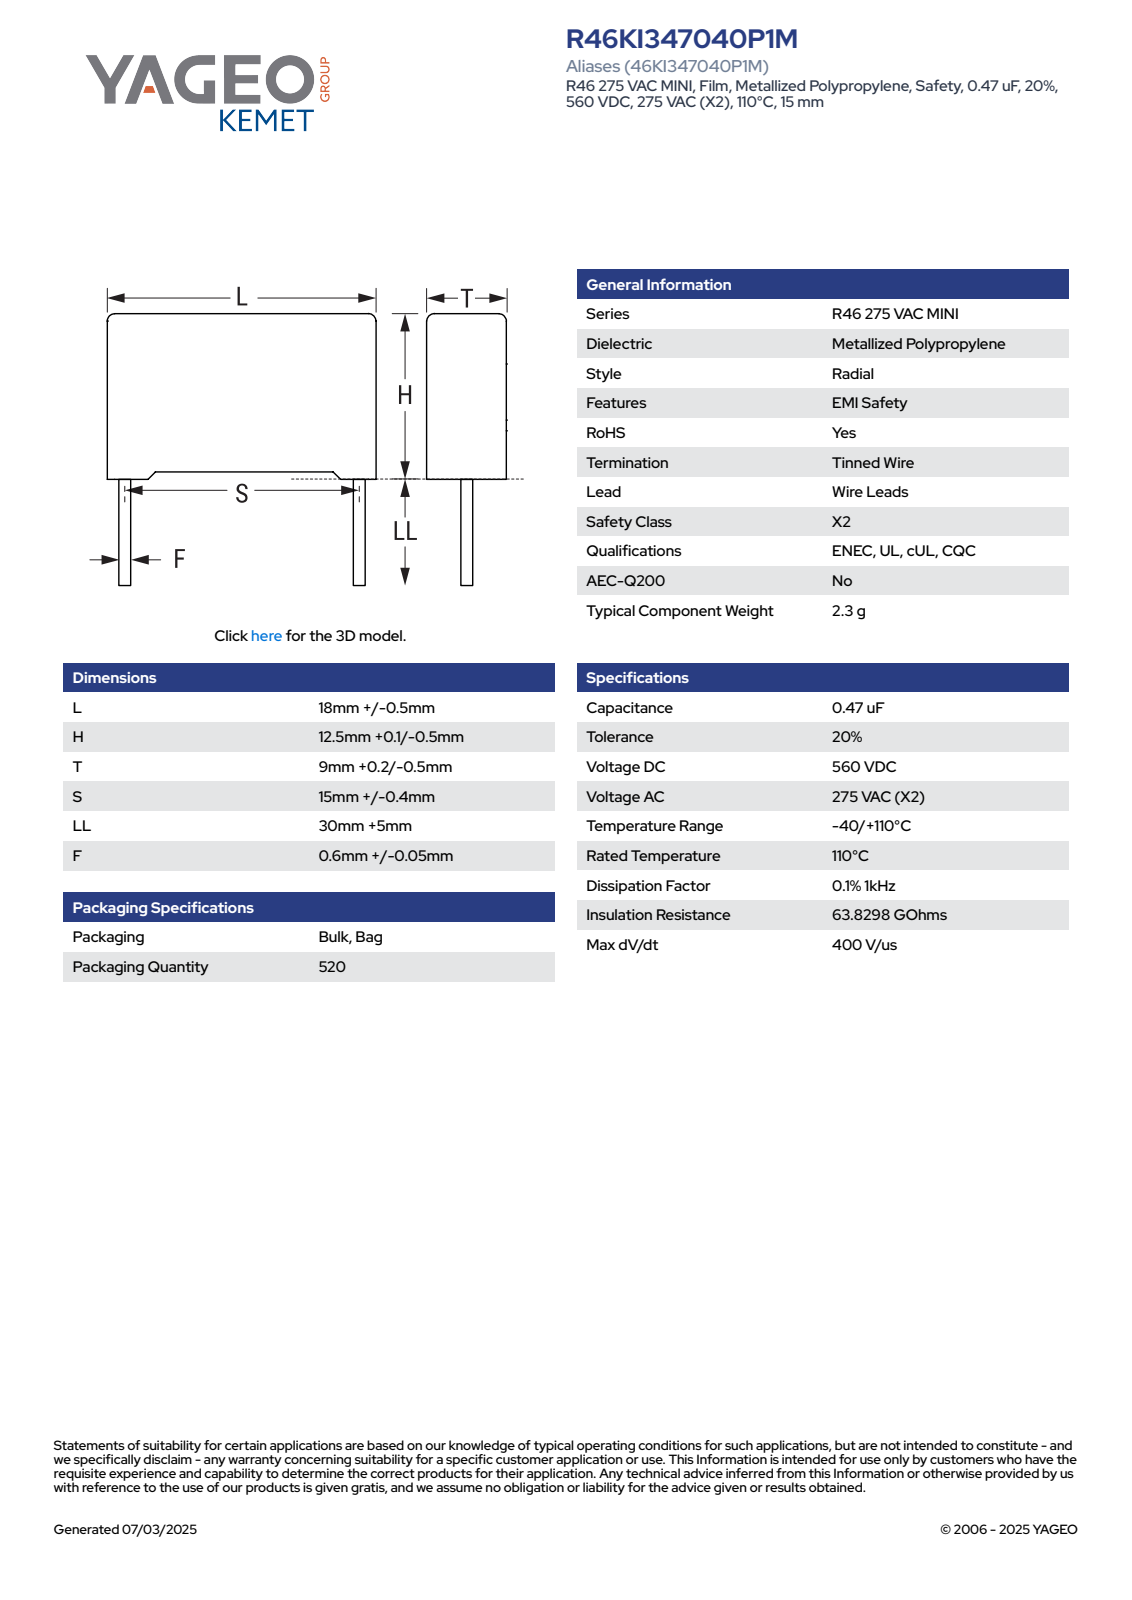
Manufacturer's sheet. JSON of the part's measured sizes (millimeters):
{"part_name": "CFR_RB2_18X12.5X9_L18.5H12.6T9.2S15LL35F0.65", "step_written_by": "SolidWorks 2021 (AUTOMOTIVE_DESIGN)", "units": "millimeters", "bodies": {"solids": 4, "faces": 85, "planar": 77, "cylindrical": 8, "other": 0}, "overall_size": [47.6, 18.5, 9.21], "volume_mm3": 2056, "surface_area_mm2": 1216, "round_bosses_or_shafts": [[0.65, 2]], "partial_cylinders_radius": [[0.5, 4]], "face_to_face_distances": [9.2, 11.85, 18.5, 0.62, 0.75, 12.6, 8.58, 0.43, 0.32, 12.17]}
